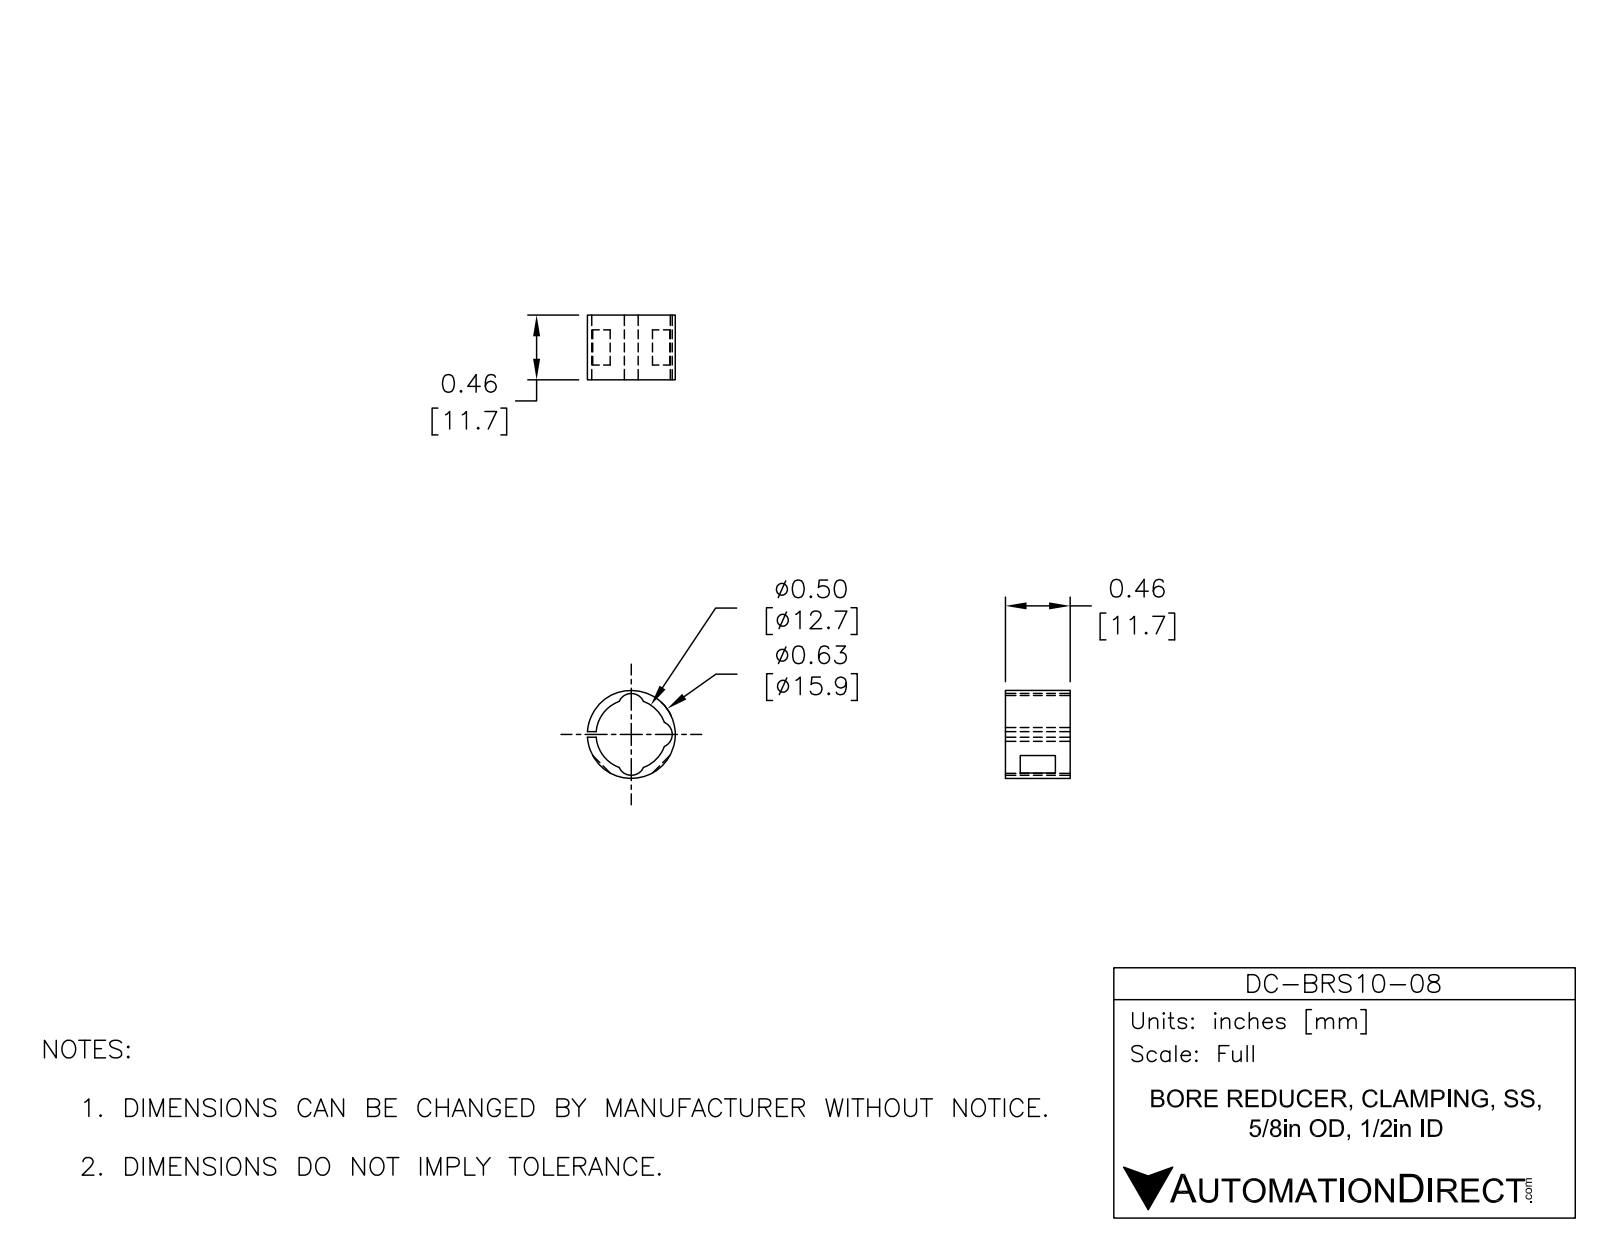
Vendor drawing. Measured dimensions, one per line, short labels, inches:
name: DC-BRS10-08
written by: SolidWorks 2015 (AUTOMOTIVE_DESIGN)
unit: in
bodies: 1 solid, 21 faces (10 planar, 11 cylindrical, 0 other)
size: 0.625 × 0.624 × 0.46
volume: 0.042 in³; area: 1.894 in²
bosses: 1× ⌀0.625
rounds: 3× R0.094, 1× R0.25
face distances: 0.46, 0.04, 0.105, 0.355, 0.25
